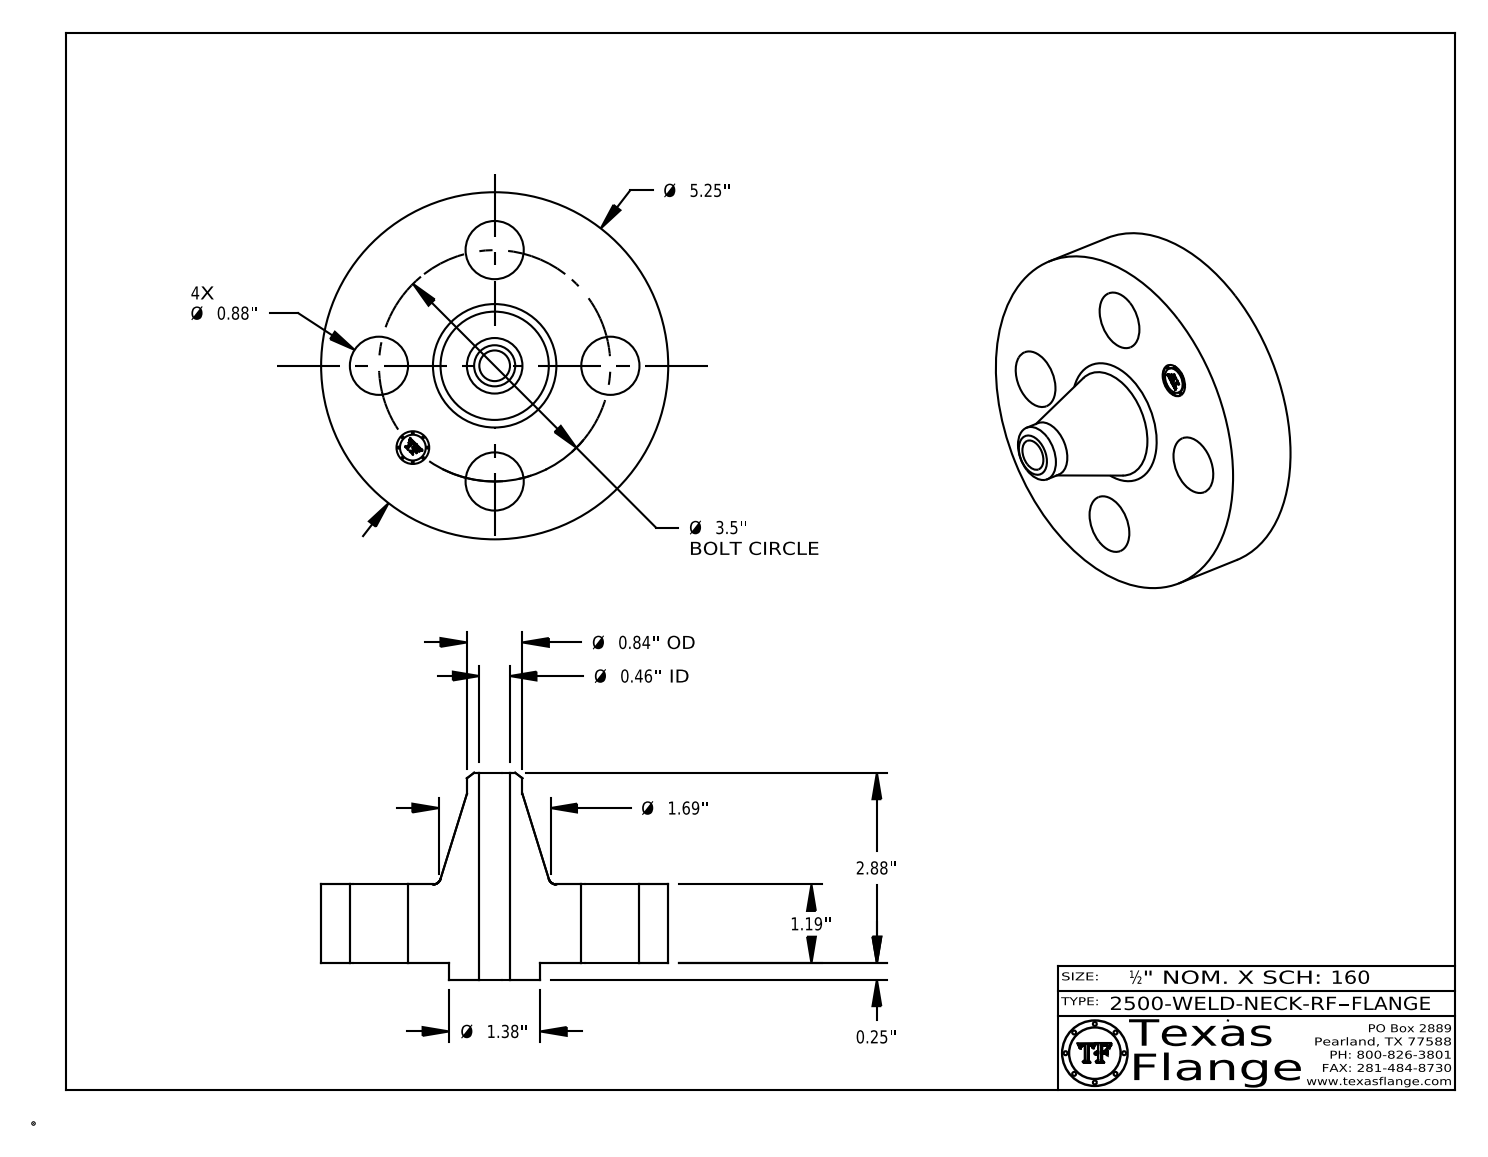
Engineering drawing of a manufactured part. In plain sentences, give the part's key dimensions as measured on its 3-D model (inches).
The part is named "2500-WELD-NECK-RF". Its 3-D file was written by "CATIA V5 STEP AP214 (AUTOMOTIVE_DESIGN)". It is 1 solid with 411 faces: 369 planar, 36 cylindrical and 6 other. Overall it measures 5.25 by 5.25 by 3.13 inches. Its volume is 24.67 cubic inches and its surface area 81.19 square inches. Round holes: 4 of diameter 0.88, 1 of diameter 0.464, 1 of diameter 0.495. Round bosses or shafts: 8 of diameter 0.03, 1 of diameter 5.25, 1 of diameter 1.38, 1 of diameter 0.84, 1 of diameter 0.39. The main face-to-face distances are 1.19, 0.25, 1.44, 3.13, 2.88, 1.69, 1.425, 1.175, 0.015, 1.705. The hole center spacings are 1.75, 2.475, 1.339, 3.233, 3.5.
